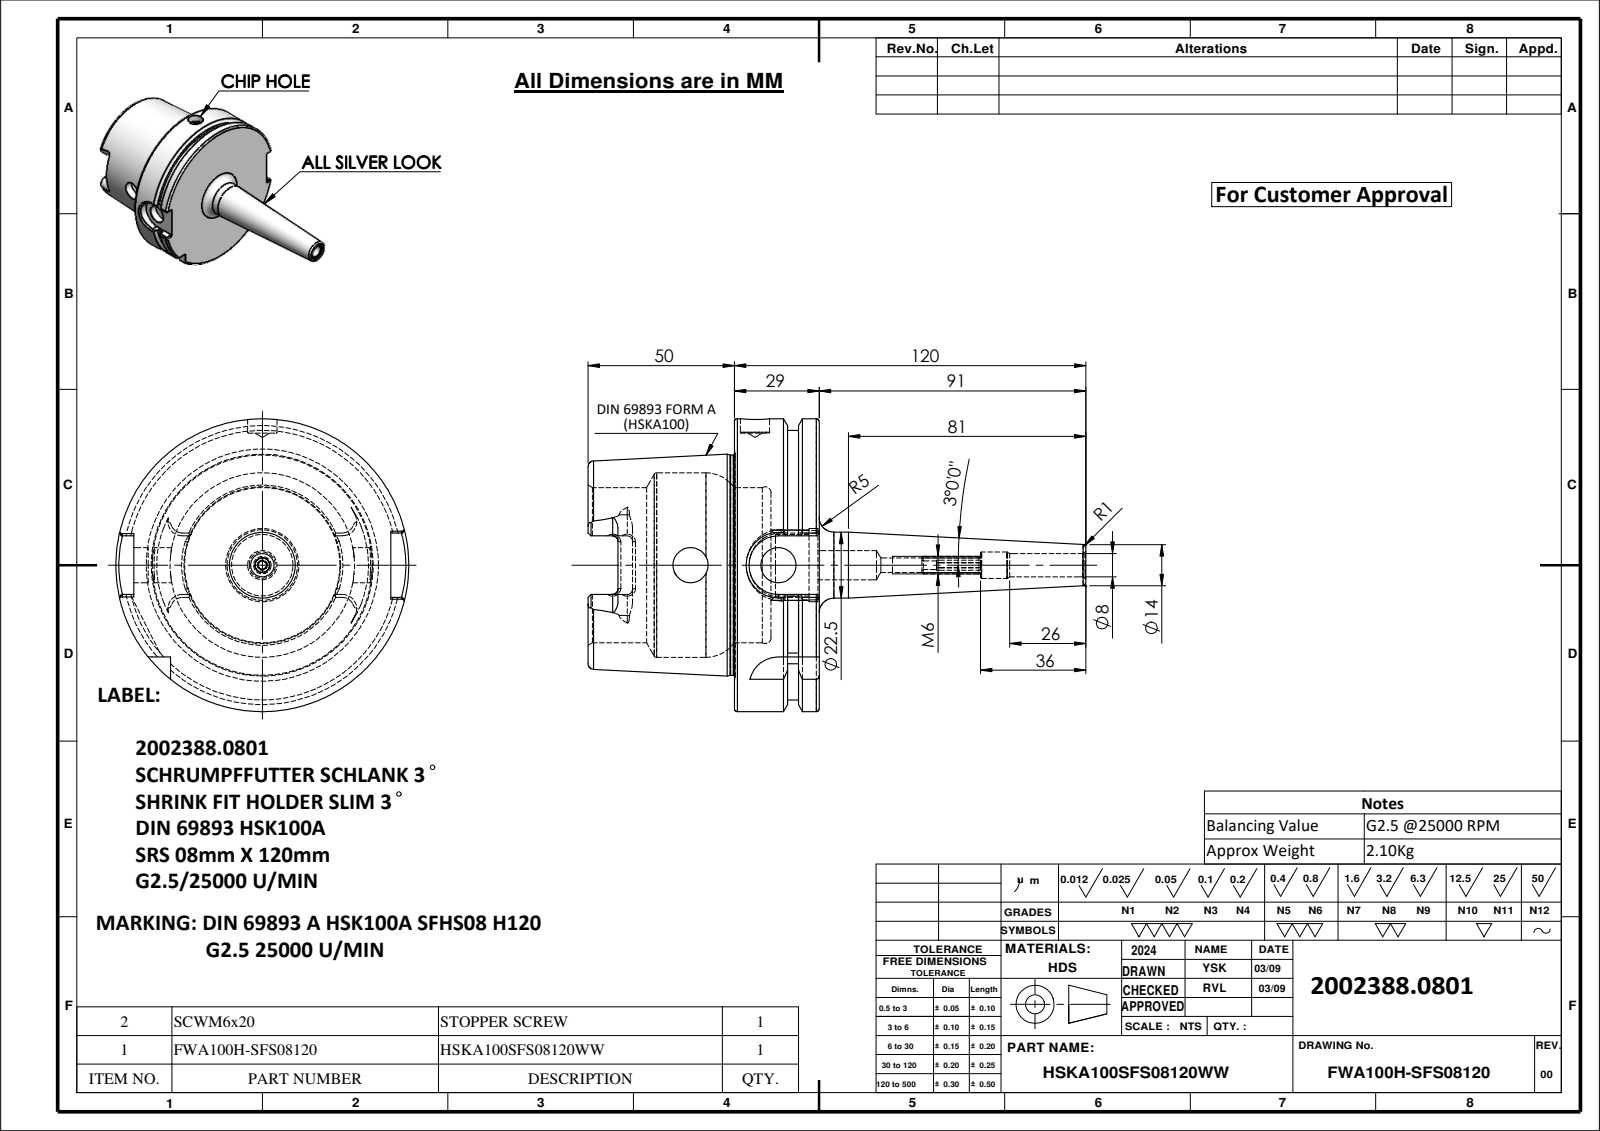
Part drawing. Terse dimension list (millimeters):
name: HSKA100SFS08120WW; FWA100H-SFS08120; SCWM6
written by: SolidWorks 2024 (CONFIG_CONTROL_DESIGN)
unit: mm
bodies: 2 solids, 205 faces (61 planar, 58 cylindrical, 86 other)
size: 170 × 100 × 100
volume: 275 780 mm³; area: 57 529 mm²
holes: 2× ⌀10, 2× ⌀12, 1× ⌀2.9, 1× ⌀5, 1× ⌀8, 1× ⌀9, 1× ⌀21, 1× ⌀25, 1× ⌀53, 1× ⌀63
bosses: 1× ⌀100, 1× ⌀92, 1× ⌀75.16, 1× ⌀22.5, 1× ⌀6
rounds: 6× R1.8, 4× R4.88, 2× R10, 1× R11
face distances: 28.95, 12.5, 16.45, 50, 62.5, 78.95, 78.5, 28.5, 16, 0.45
hole spacings: 30
